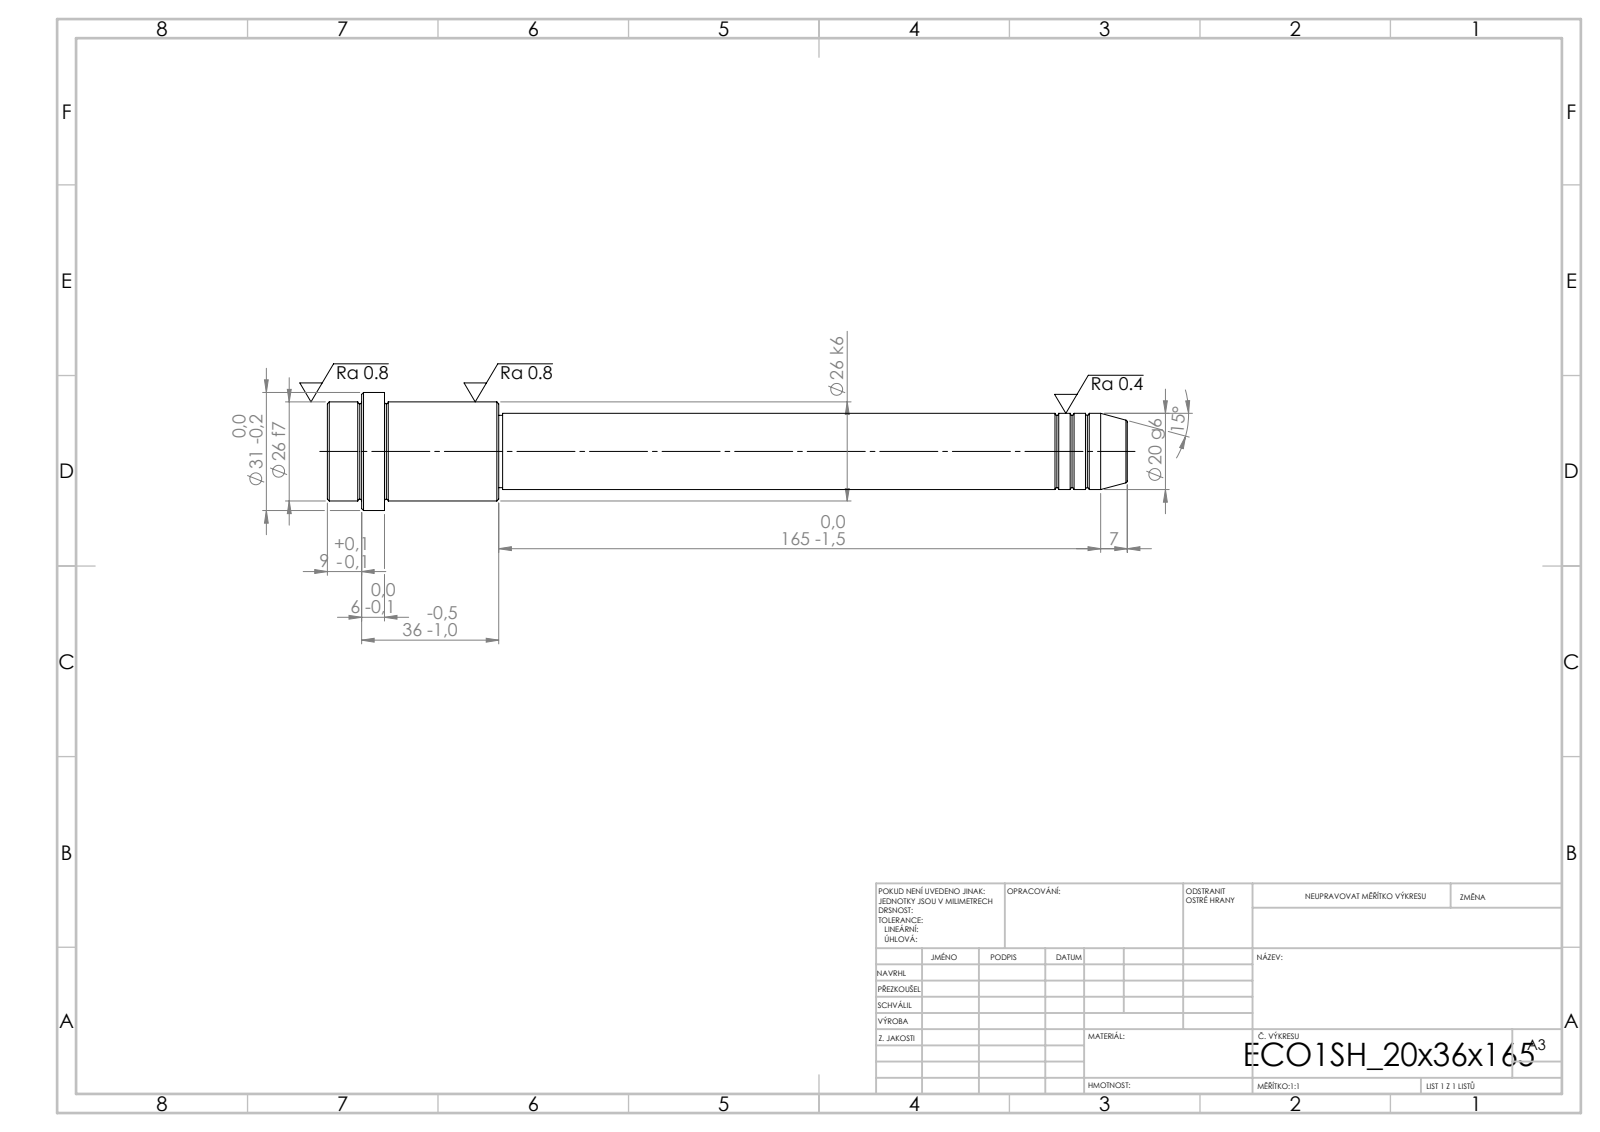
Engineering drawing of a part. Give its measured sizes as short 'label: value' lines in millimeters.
written by: SolidWorks 2019 (CONFIG_CONTROL_DESIGN)
unit: mm
bodies: 1 solid, 52 faces (6 planar, 16 cylindrical, 30 other)
size: 210 × 31 × 31
volume: 76 485 mm³; area: 15 673 mm²
bosses: 1× ⌀31, 1× ⌀26, 1× ⌀20, 1× ⌀19
face distances: 15, 30, 45, 165, 195, 210, 201, 36, 6, 9
